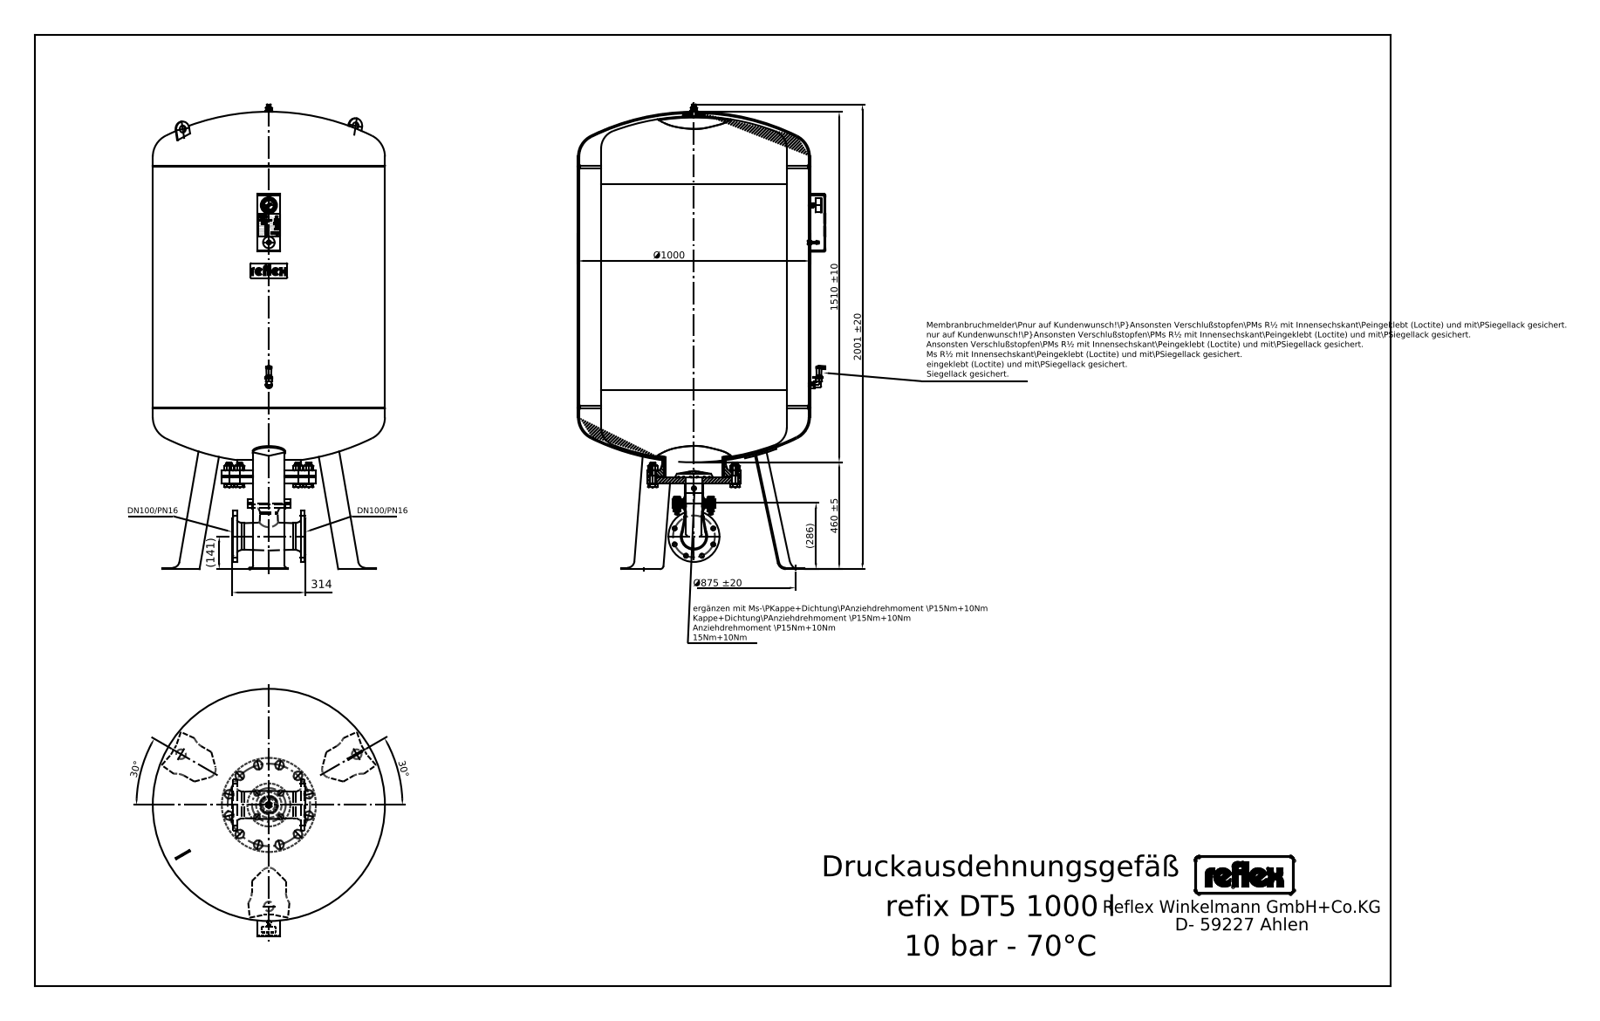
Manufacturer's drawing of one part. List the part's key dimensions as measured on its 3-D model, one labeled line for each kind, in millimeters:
STEP written by: Mechanical Desktop 2008 (CONFIG_CONTROL_DESIGN)
Units: millimetres
Bodies: 31 solids, 795 faces (417 planar, 195 cylindrical, 183 other)
Overall size (bounding box): 2000 × 1066 × 1000
Volume: 1 095 000 000 mm³ · Surface area: 10 760 000 mm²
Round holes (diameter × count): ⌀19 ×8, ⌀10 ×1, ⌀30 ×1, ⌀50 ×1, ⌀69 ×1, ⌀114.3 ×1, ⌀260.4 ×1
Round bosses / shafts (diameter × count): ⌀16 ×17, ⌀28 ×2, ⌀26 ×2, ⌀20 ×2, ⌀1000 ×1, ⌀405 ×1, ⌀273 ×1, ⌀220 ×1
Partial cylindrical surfaces — rounded edges, fillets, slot ends (radius × count): R25 ×18, R5.62 ×4, R2.25 ×3, R9 ×3, R1 ×2, R3.84 ×2, R5 ×2, R6.75 ×2
Main face-to-face distances: 1075, 26, 274.5, 1349.5, 300.5, 1375.5, 31, 57, 243.5, 1318.5
Hole centre spacings: 90, 127.28, 166.3, 68.88, 68.89, 180, 82.33, 515.5
